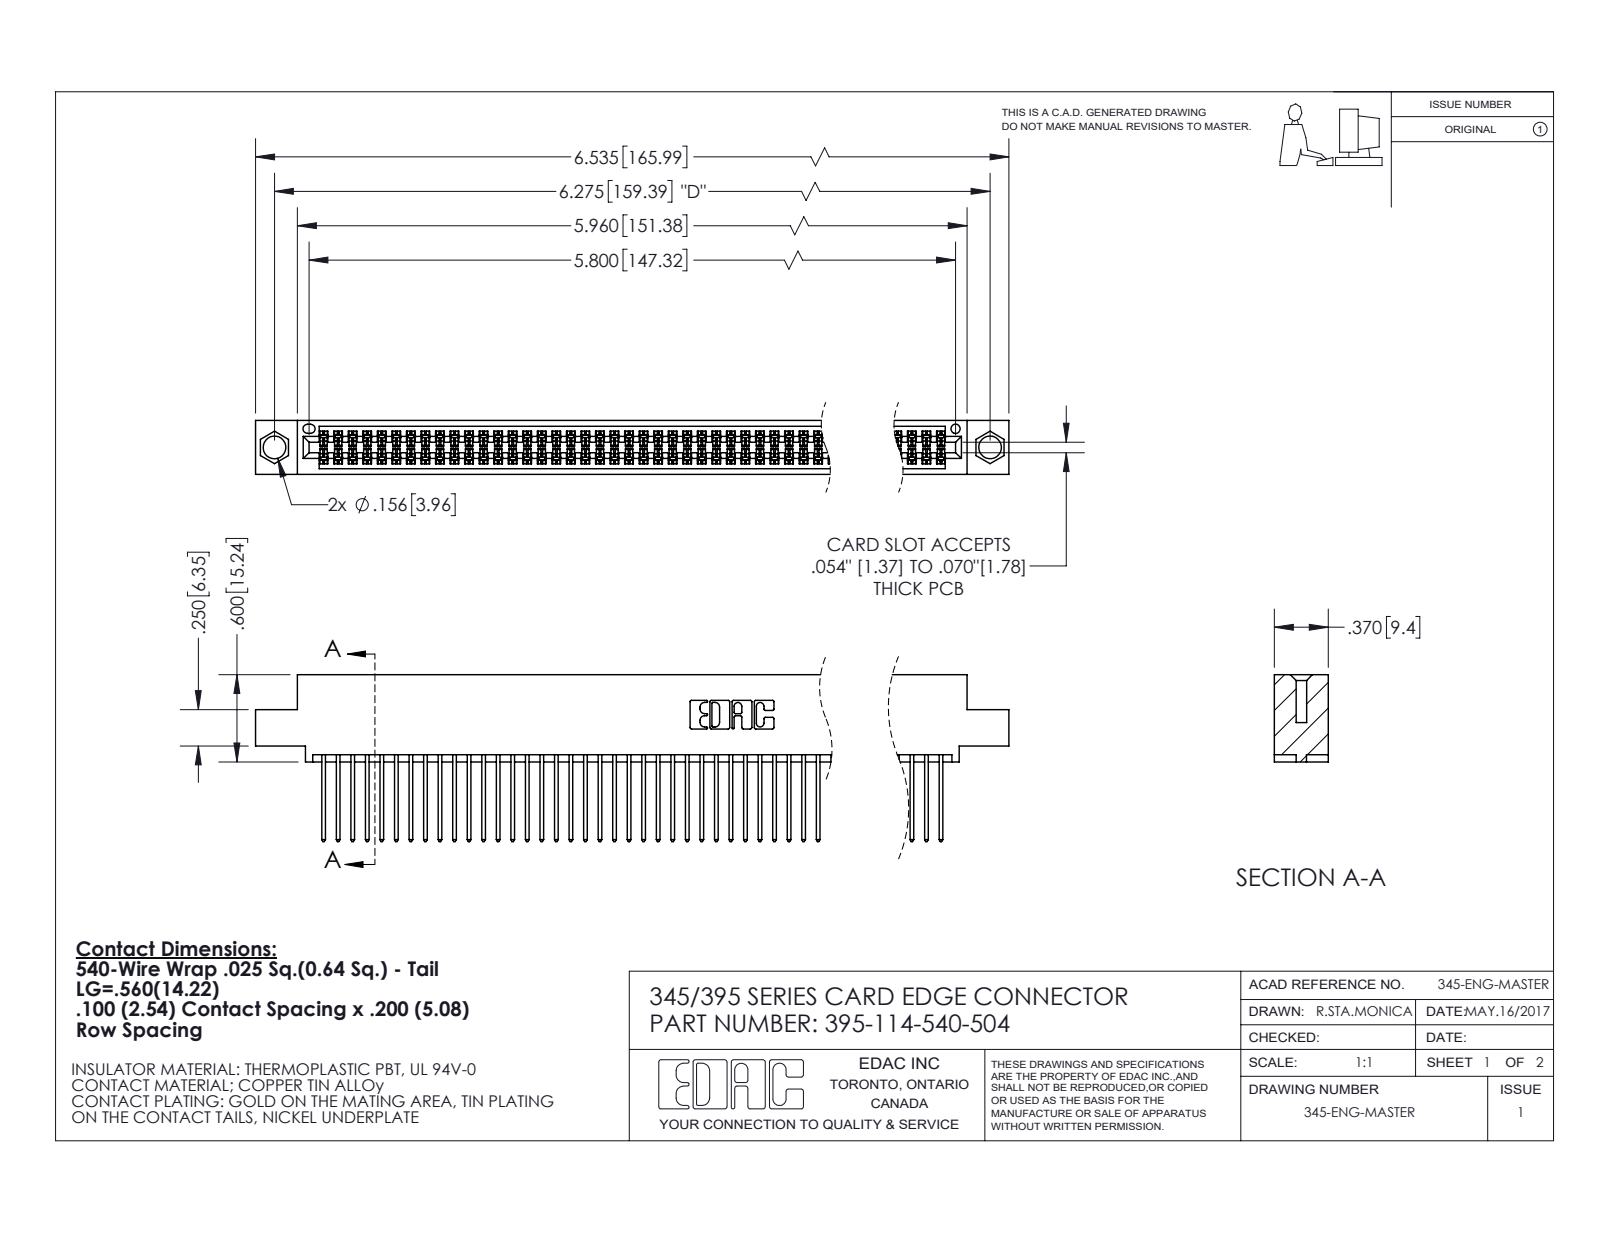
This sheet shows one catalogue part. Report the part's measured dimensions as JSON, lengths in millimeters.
{"part_name": "345 Part_0.110 Offset - 0.156 Dia-TI; 395-114-540-504; 345-292-001_345-293-140", "step_written_by": "SolidWorks 2020 (CONFIG_CONTROL_DESIGN)", "units": "millimeters", "bodies": {"solids": 115, "faces": 5844, "planar": 3860, "cylindrical": 1984, "other": 0}, "overall_size": [166, 29.1, 9.4], "volume_mm3": 16520, "surface_area_mm2": 26650, "round_holes": [[4, 2], [1.6, 1]], "partial_cylinders_radius": [[0.2, 228], [0.3, 114], [0.3, 22], [0.2, 6], [0.8, 6], [0.7, 3], [0.4, 2], [0.5, 2]], "face_to_face_distances": [7.6, 1.8, 5.1, 2.5, 6.9, 0.6, 9.4, 5.7, 4.4, 3.8], "hole_center_spacings": [6.9, 153.4, 159.4]}
